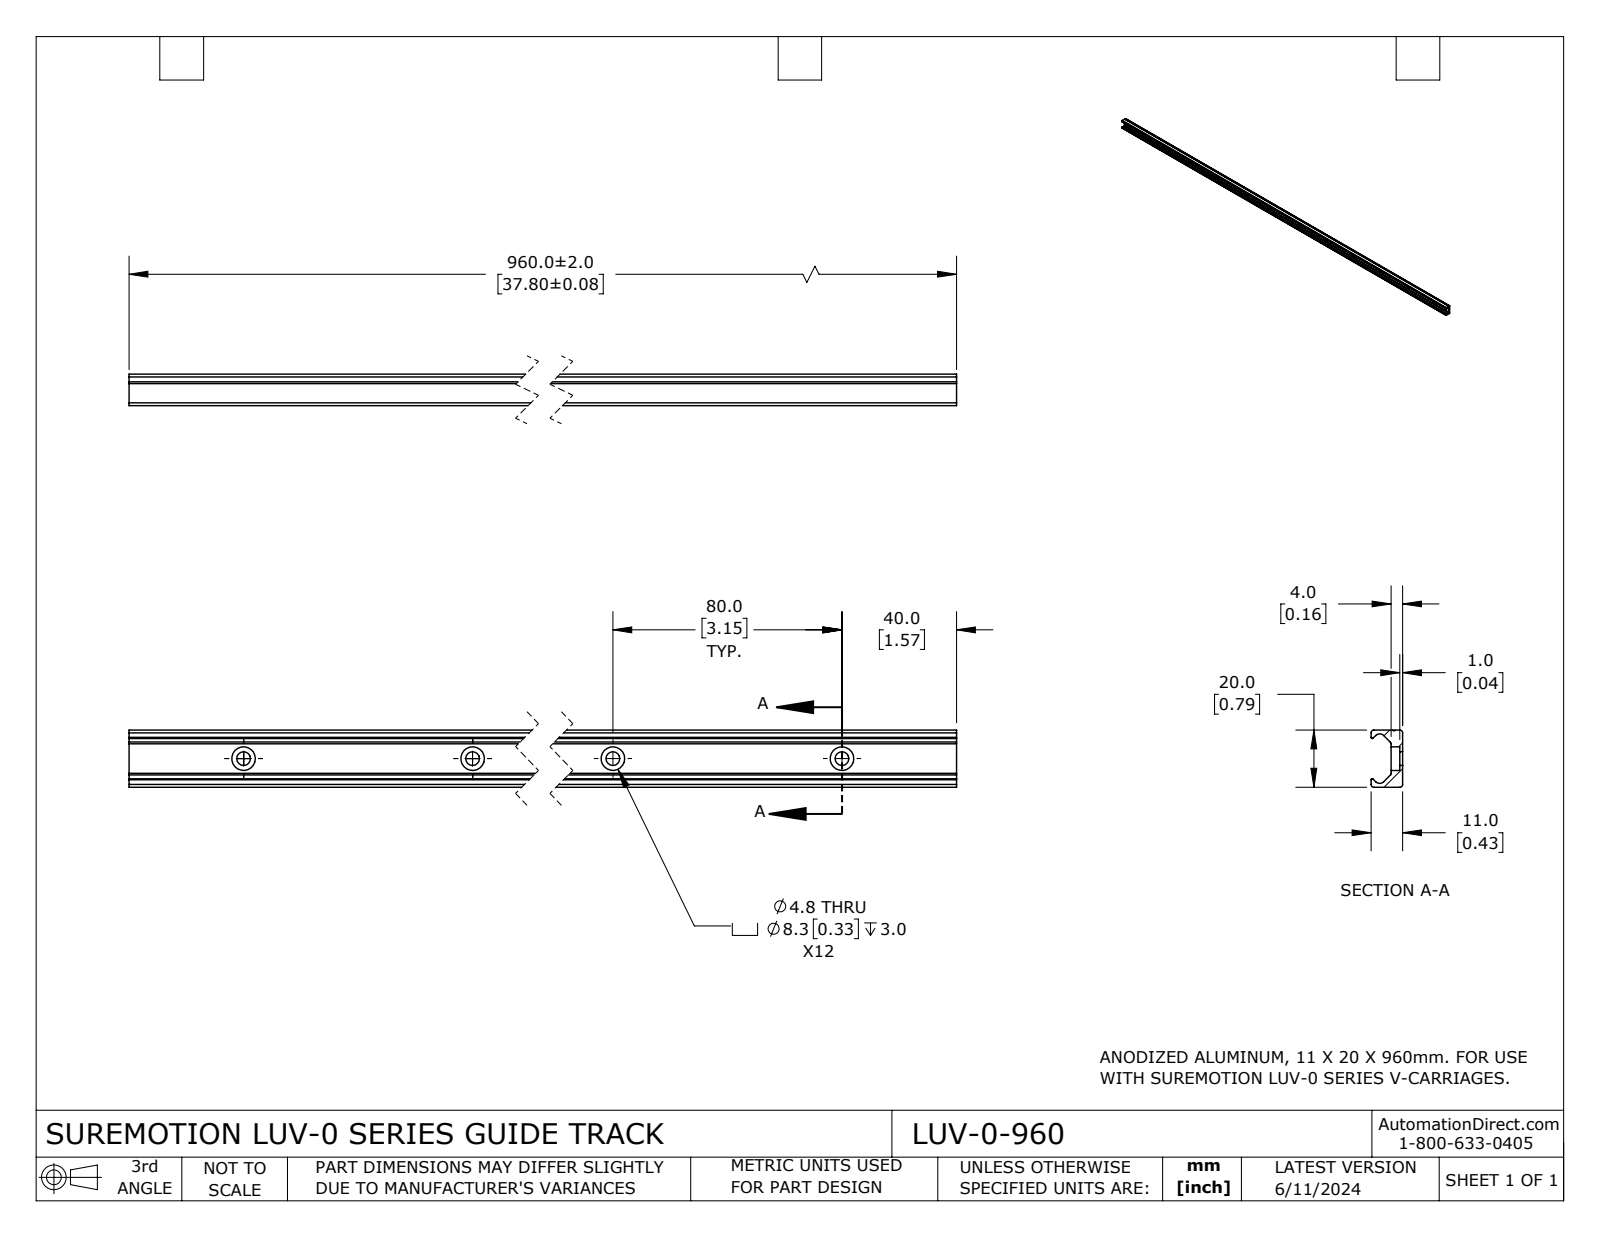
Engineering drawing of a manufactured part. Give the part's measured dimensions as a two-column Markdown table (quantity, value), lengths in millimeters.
| quantity | value |
| --- | --- |
| part name | LUV-0-960 |
| STEP written by | SolidWorks 2023 (CONFIG_CONTROL_DESIGN) |
| units | millimeters |
| bodies | 1 solid, 86 faces (25 planar, 61 cylindrical, 0 other) |
| overall size | 960 × 19.99 × 11 |
| volume | 105 955 mm³ |
| surface area | 72 699 mm² |
| round holes (diameter × count) | 4.8 × 12, 8.25 × 7, 8.26 × 5 |
| partial cylindrical surfaces (radius × count) | 0.99 × 4, 0.38 × 2, 0.4 × 2, 0.79 × 2, 1.98 × 2, 0.33 × 1 |
| main face-to-face distances | 4.01, 20, 11, 6.99, 13.4, 1.01, 3, 9.99, 960 |
| hole center spacings | 80, 160, 240, 320, 400, 480, 560, 640 |
